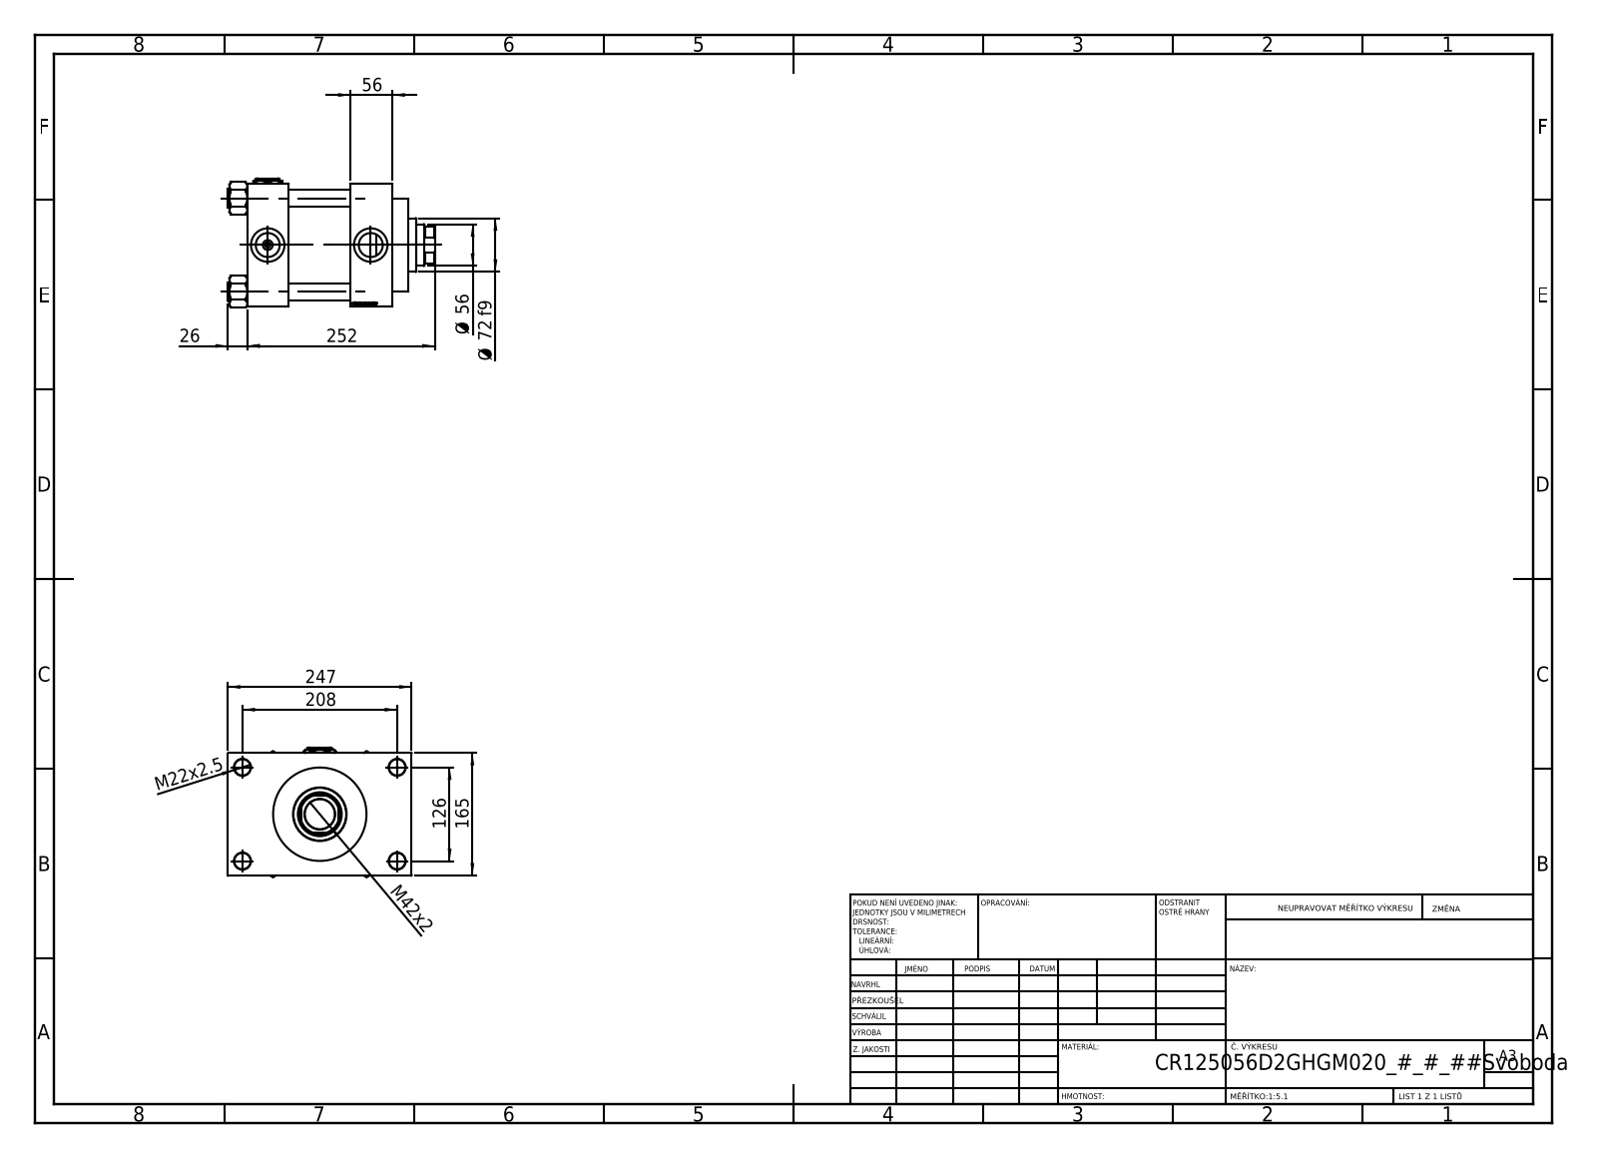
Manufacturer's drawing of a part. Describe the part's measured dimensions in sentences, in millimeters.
The part is named "Zatka_pro_OIL_PORT; V215CR_D_TYCINKA; NUT_M5_D; V215_VC_A (+2 more)". Its 3-D file was written by "SolidWorks 2019 (CONFIG_CONTROL_DESIGN)". It is 12 solids with 1201 faces: 568 planar, 93 cylindrical and 540 other. Overall it measures 278 by 247 by 174.07 millimeters. Its volume is 4 920 000 cubic millimeters and its surface area 539 927 square millimeters. Round holes: 8 of diameter 22, 3 of diameter 7, 3 of diameter 32.24, 3 of diameter 45, 1 of diameter 40.5, 1 of diameter 56, 1 of diameter 59, 1 of diameter 96, 1 of diameter 125, 1 of diameter 125.5. Round bosses or shafts: 4 of diameter 25, 1 of diameter 131, 1 of diameter 72. Partial cylindrical surfaces (rounded edges, fillets, slot ends): 1 of radius 27. The main face-to-face distances are 165, 84, 55, 139, 56, 195, 140, 41, 206, 173.74. The hole center spacings are 41.05, 89.02, 121.59, 125.9, 132.47, 166.95, 209.13, 126.
